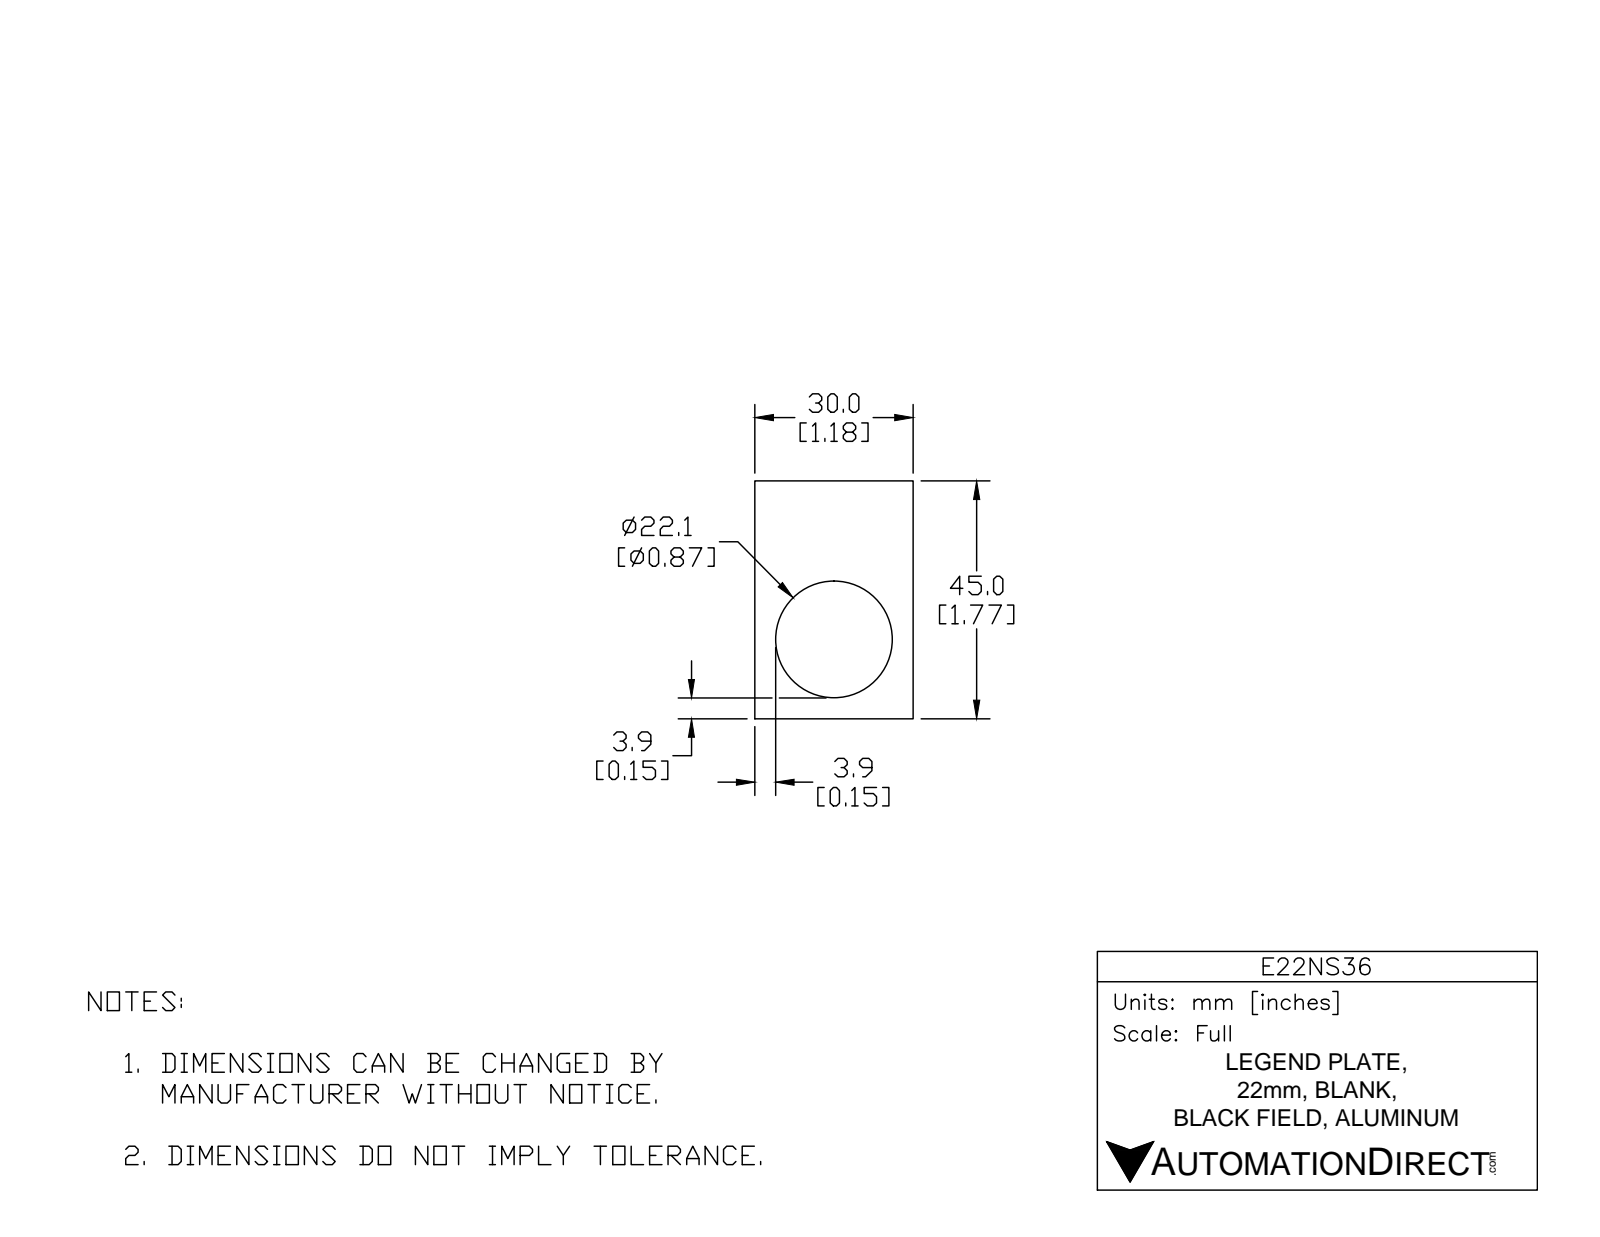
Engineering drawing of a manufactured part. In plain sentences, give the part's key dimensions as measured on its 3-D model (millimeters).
The part is named "E22NS36". Its 3-D file was written by "SolidWorks 2017 (AUTOMOTIVE_DESIGN)". It is 1 solid with 12 faces: 9 planar, 3 cylindrical and 0 other. Overall it measures 45 by 30 by 1.3 millimeters. Its volume is 1 255 cubic millimeters and its surface area 2 218 square millimeters. Round holes: 1 of diameter 22.2. The main face-to-face distances are 1.3, 30, 45, 4.7, 40.3, 13.4, 16.6, 3.2.
